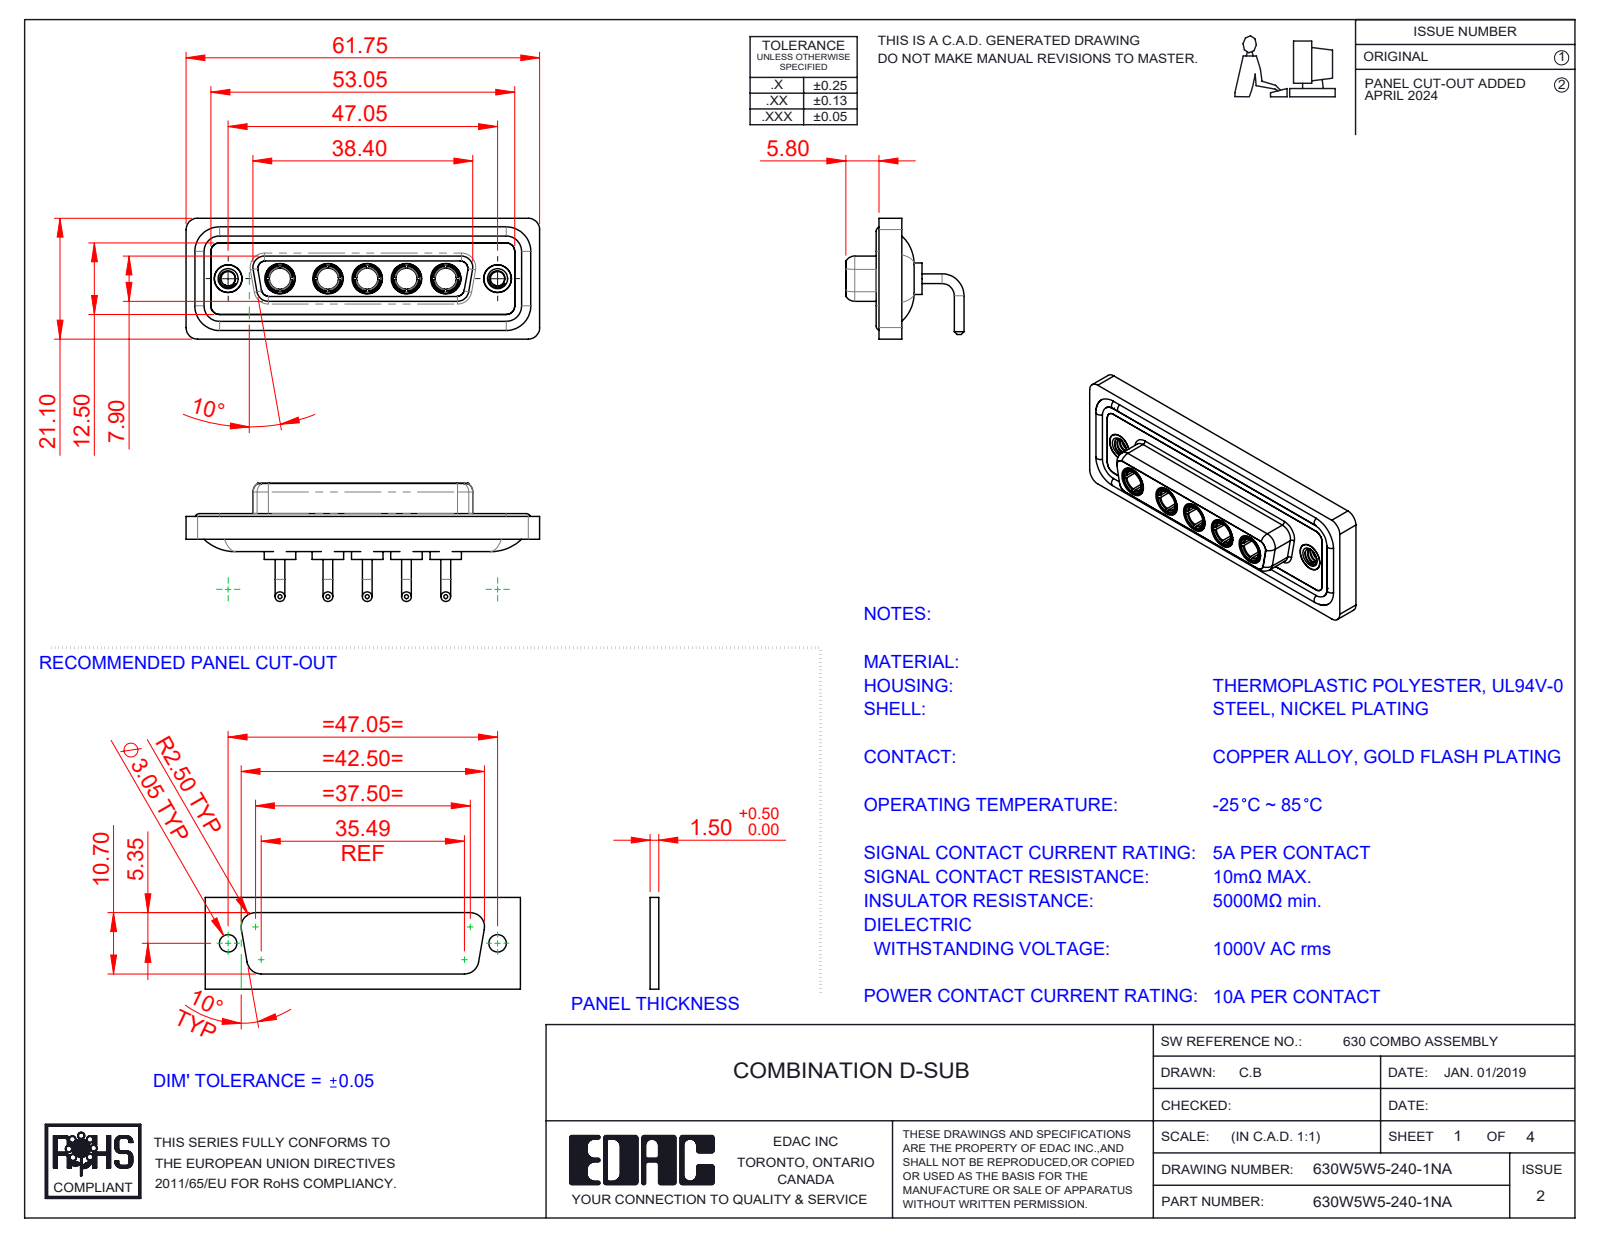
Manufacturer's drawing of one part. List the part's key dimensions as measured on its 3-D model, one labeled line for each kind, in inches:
Part name (STEP PRODUCT): 630Combo Threaded Rivet_A; Power Socket_10A RA; 630Combo Housing_5W5; 630Combo Shell Rear_25 Contacts (+3 more)
STEP written by: SolidWorks 2023 (CONFIG_CONTROL_DESIGN)
Units: inches
Bodies: 17 solids, 770 faces (250 planar, 311 cylindrical, 209 other)
Overall size (bounding box): 2.431 × 0.831 × 0.813
Volume: 0.497 in³ · Surface area: 21.02 in²
Round holes (diameter × count): ⌀0.191 ×7, ⌀0.146 ×5, ⌀0.209 ×5, ⌀0.098 ×2, ⌀0.157 ×2, ⌀0.159 ×2, ⌀0.197 ×2
Round bosses / shafts (diameter × count): ⌀0.067 ×10, ⌀0.217 ×5, ⌀0.205 ×5, ⌀0.195 ×5, ⌀0.187 ×5, ⌀0.148 ×5, ⌀0.063 ×4, ⌀0.195 ×2
Partial cylindrical surfaces — rounded edges, fillets, slot ends (radius × count): R0.059 ×18, R0.079 ×18, R0.053 ×8, R0.063 ×8, R0.083 ×5, R0.01 ×4, R0.02 ×4, R0.024 ×4
Main face-to-face distances: 0.016, 0.071, 0.161, 0.043, 0.059, 0.098, 0.122, 0.146, 0.063, 0.053
Hole centre spacings: 0.27, 0.356, 1.496, 0.27, 0.33, 0.54, 0.541, 0.6
